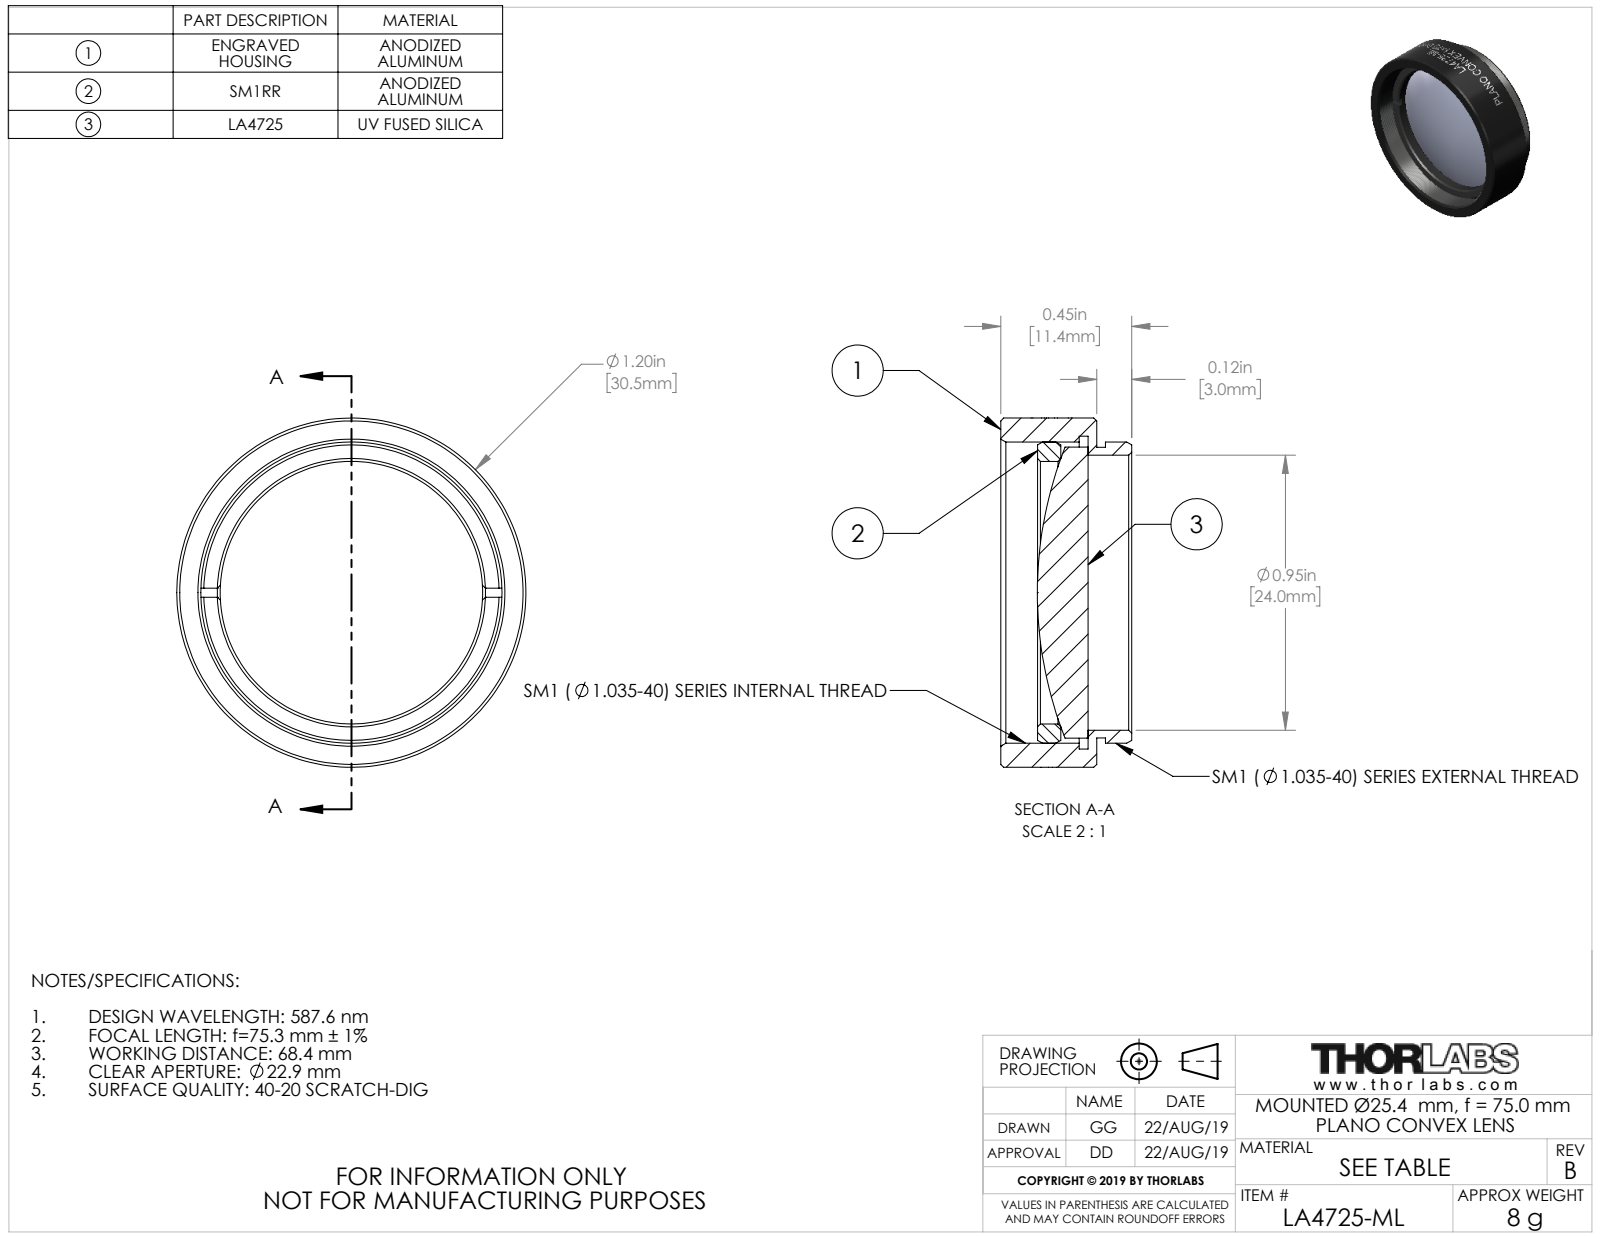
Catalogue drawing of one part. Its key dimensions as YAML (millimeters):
part_name: "24454-E0W"
step_written_by: "SolidWorks 2018 (CONFIG_CONTROL_DESIGN)"
units: millimeters
bodies: {solids: 3, faces: 115, planar: 20, cylindrical: 71, other: 24}
overall_size: [30.48, 30.48, 11.43]
volume: 3716
surface_area: 4331
round_holes:
  - {diameter: 22.91, count: 1}
  - {diameter: 24, count: 1}
  - {diameter: 27.3, count: 1}
round_bosses_or_shafts:
  - {diameter: 30.48, count: 1}
  - {diameter: 26.29, count: 1}
  - {diameter: 25.4, count: 1}
  - {diameter: 25.37, count: 1}
face_to_face_distances: [0.76, 8.38, 7.62, 3.13, 2.37, 5.25, 5.17, 4.41, 2.04, 3.21]
